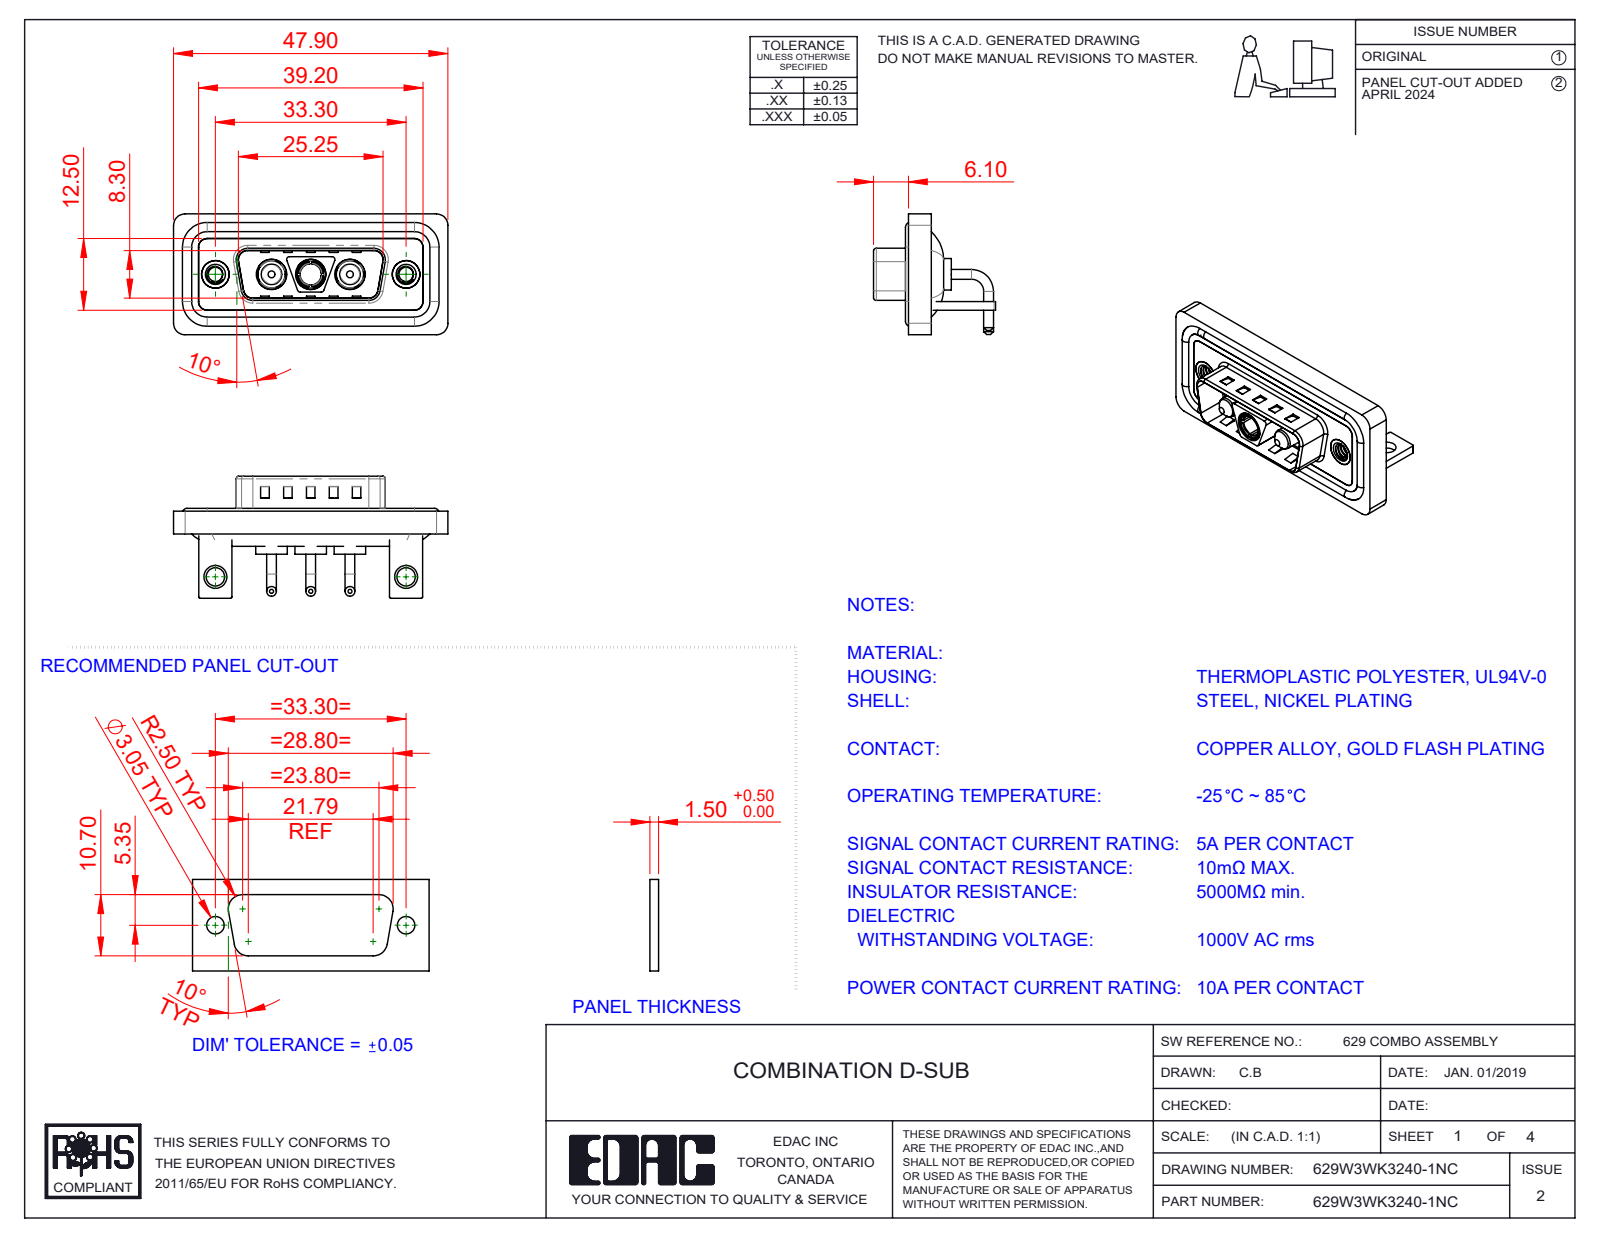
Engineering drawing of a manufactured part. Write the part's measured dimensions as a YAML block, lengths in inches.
part_name: "629Combo Shell Front_15 Contacts; 629Combo Housing_3WK3; Power Pin_10A RA; 629Combo Shell Rear_15 Contacts (+5 more)"
step_written_by: "SolidWorks 2023 (CONFIG_CONTROL_DESIGN)"
units: inches
bodies: {solids: 15, faces: 659, planar: 251, cylindrical: 274, other: 134}
overall_size: [1.886, 0.839, 0.831]
volume: 0.365
surface_area: 15.27
round_holes:
  - {diameter: 0.191, count: 3}
  - {diameter: 0.209, count: 3}
  - {diameter: 0.098, count: 2}
  - {diameter: 0.126, count: 2}
  - {diameter: 0.157, count: 2}
  - {diameter: 0.189, count: 2}
  - {diameter: 0.197, count: 2}
  - {diameter: 0.146, count: 1}
round_bosses_or_shafts:
  - {diameter: 0.067, count: 6}
  - {diameter: 0.063, count: 4}
  - {diameter: 0.217, count: 3}
  - {diameter: 0.205, count: 3}
  - {diameter: 0.187, count: 3}
  - {diameter: 0.148, count: 3}
  - {diameter: 0.193, count: 2}
  - {diameter: 0.142, count: 2}
partial_cylinders:
  - {radius: 0.079, count: 21}
  - {radius: 0.059, count: 18}
  - {radius: 0.01, count: 16}
  - {radius: 0.02, count: 13}
  - {radius: 0.063, count: 8}
  - {radius: 0.024, count: 4}
  - {radius: 0.026, count: 4}
  - {radius: 0.035, count: 4}
face_to_face_distances: [0.016, 0.059, 0.031, 0.114, 0.043, 0.083, 0.146, 0.063, 0.047, 0.177]
hole_center_spacings: [0.27, 0.386, 0.656, 0.925, 1.311, 0.539]
